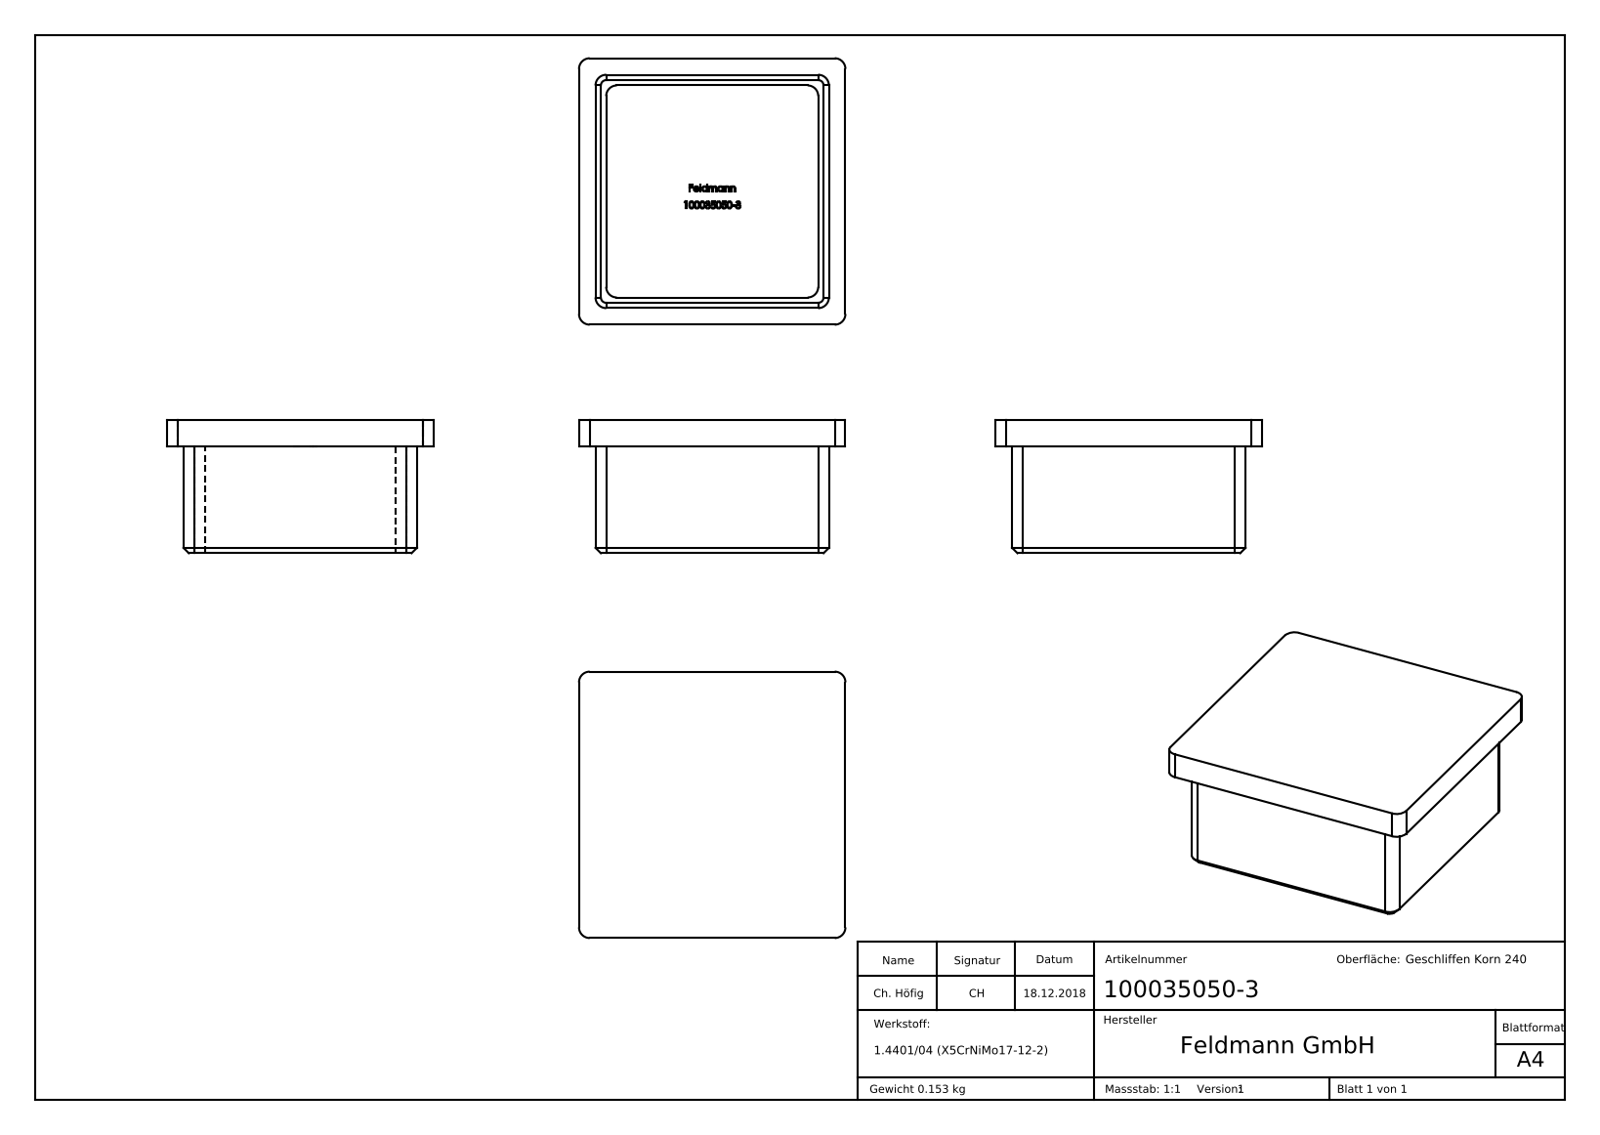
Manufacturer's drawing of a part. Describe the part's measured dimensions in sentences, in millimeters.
The part is named "100035050-3". Its 3-D file was written by "SolidWorks 2015 (CONFIG_CONTROL_DESIGN)". It is 1 solid with 282 faces: 129 planar, 12 cylindrical and 141 other. Overall it measures 50 by 50 by 25 millimeters. Its volume is 19 085 cubic millimeters and its surface area 12 436 square millimeters. Partial cylindrical surfaces (rounded edges, fillets, slot ends): 12 of radius 2. The main face-to-face distances are 2, 41.8, 5, 43.8, 39.8, 3.1, 5.1, 44.9, 46.9, 50.
